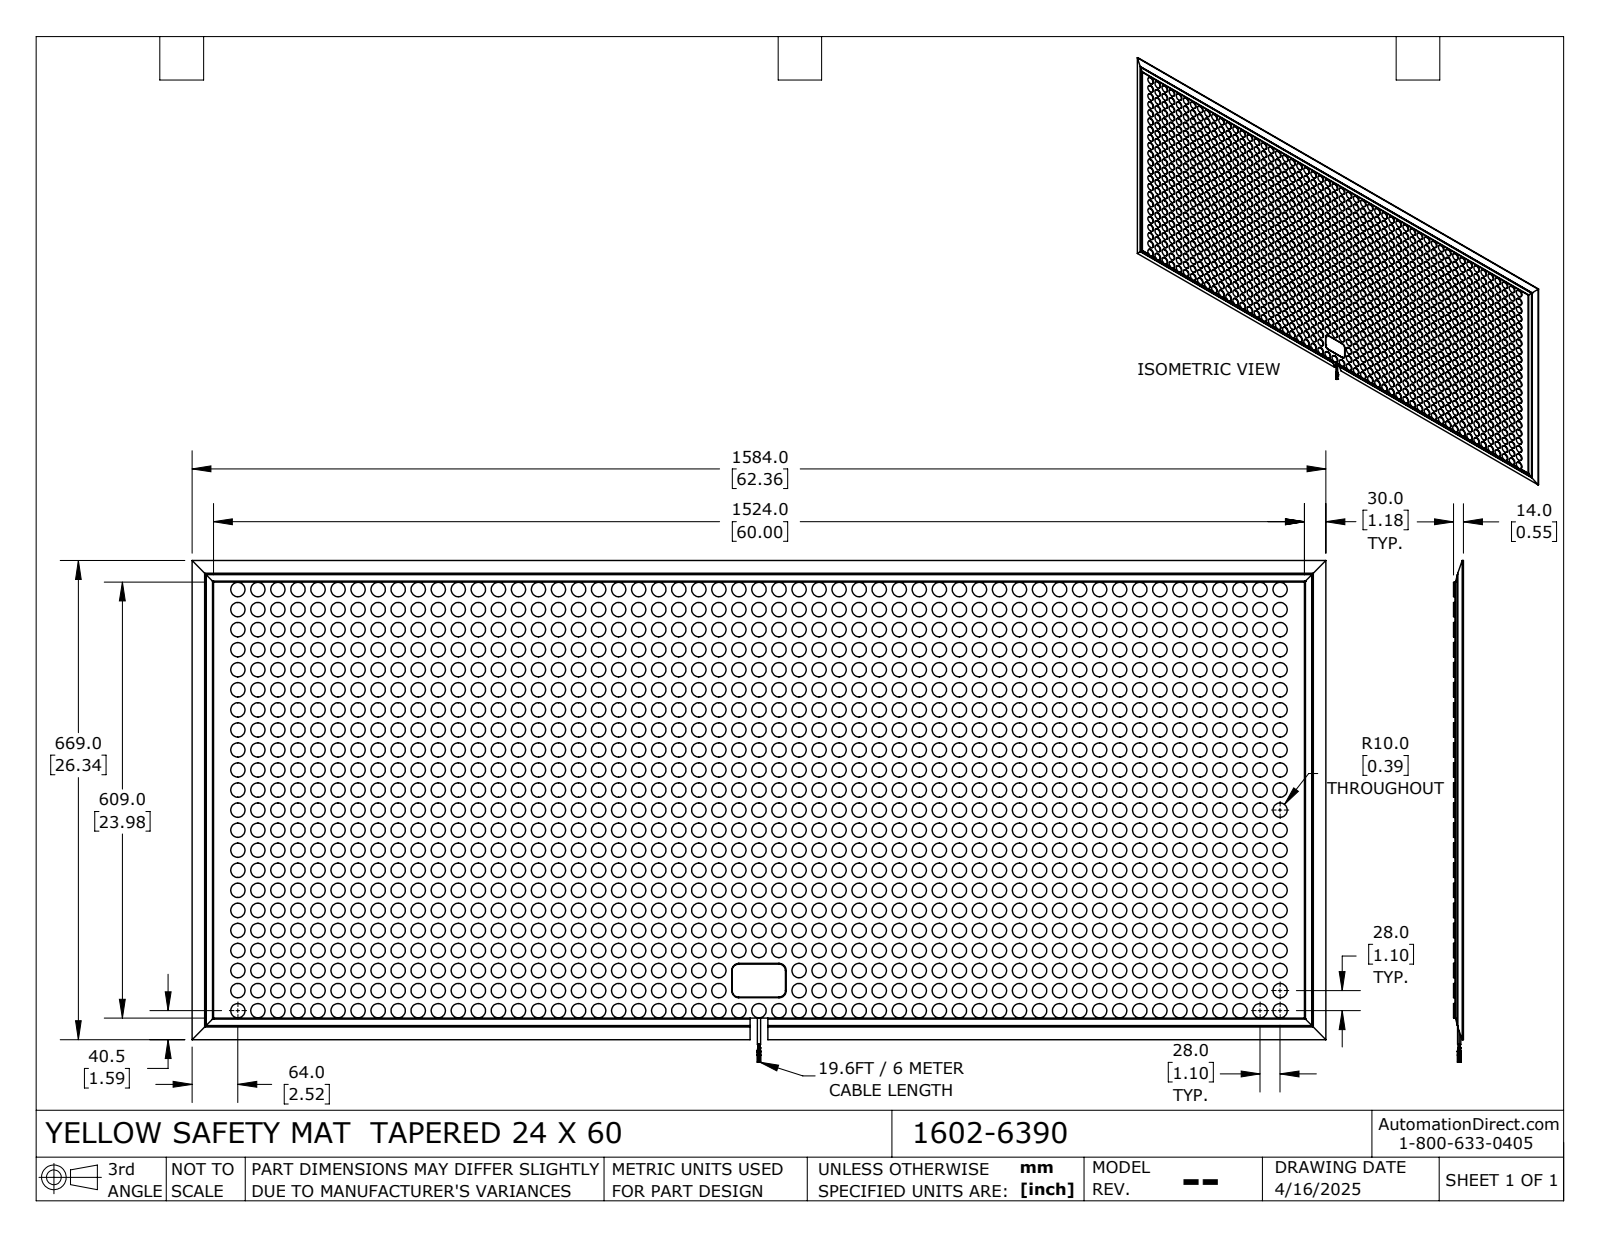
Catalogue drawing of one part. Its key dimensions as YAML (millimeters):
part_name: "1602-4092"
step_written_by: "SolidWorks 2021 (AUTOMOTIVE_DESIGN)"
units: millimeters
bodies: {solids: 1165, faces: 4841, planar: 2398, cylindrical: 2402, other: 41}
overall_size: [1584, 700.5, 14]
volume: 12590000
surface_area: 3125000
round_bosses_or_shafts:
  - {diameter: 20, count: 1160}
  - {diameter: 1.2, count: 20}
  - {diameter: 0.8, count: 8}
  - {diameter: 4.4, count: 1}
partial_cylinders:
  - {radius: 10, count: 6}
  - {radius: 1, count: 4}
face_to_face_distances: [12, 2, 14, 609, 1524, 30, 3.4, 1.4, 10.6, 3.5]
